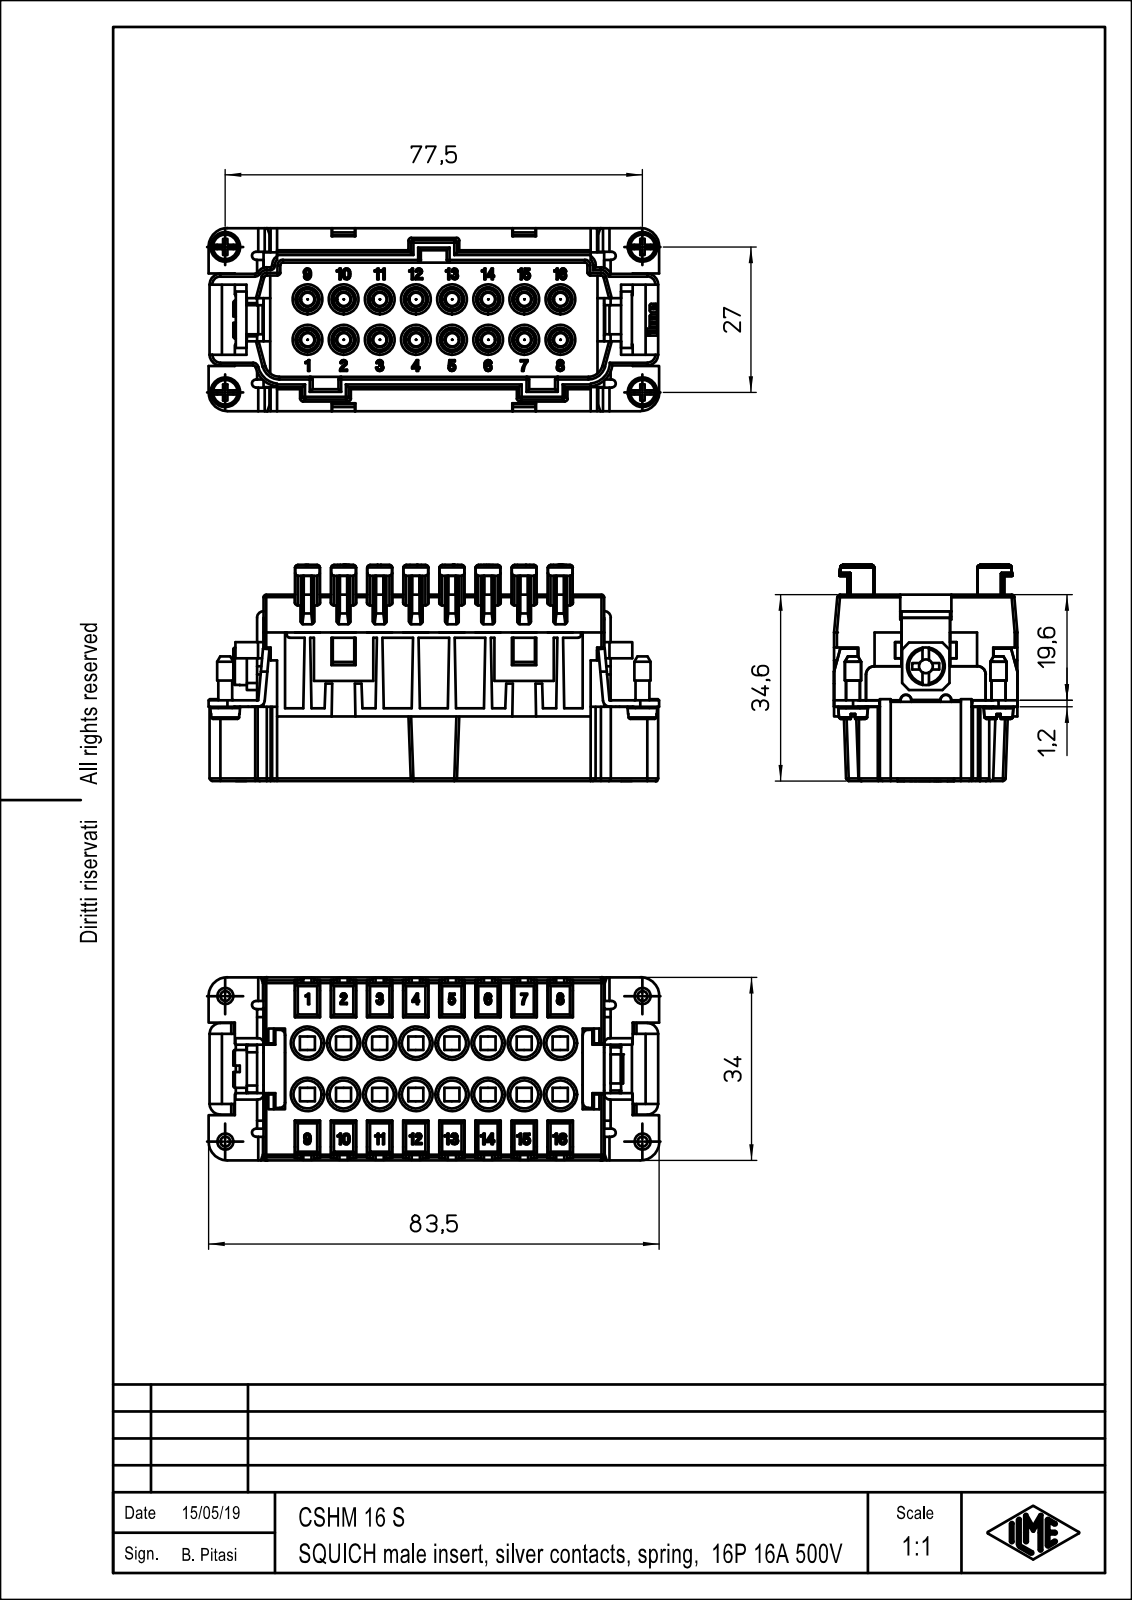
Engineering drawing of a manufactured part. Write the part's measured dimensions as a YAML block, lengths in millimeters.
part_name: "CSHM_16_S"
step_written_by: "Creo Elements/Direct Modeling 20.1B 02-Apr-2019 (C) Parametric Technology GmbH (AUTOMOTIVE_DESIGN)"
units: millimeters
bodies: {solids: 1, faces: 2082, planar: 1264, cylindrical: 557, other: 261}
overall_size: [83.6, 40.1, 34]
volume: 48900
surface_area: 30929
round_holes:
  - {diameter: 5.2, count: 16}
  - {diameter: 2.8, count: 4}
  - {diameter: 2.58, count: 1}
  - {diameter: 4.2, count: 1}
round_bosses_or_shafts:
  - {diameter: 2.48, count: 16}
  - {diameter: 5.5, count: 4}
  - {diameter: 3, count: 4}
  - {diameter: 2.6, count: 4}
  - {diameter: 7, count: 1}
  - {diameter: 6, count: 1}
  - {diameter: 4, count: 1}
partial_cylinders:
  - {radius: 0.5, count: 169}
  - {radius: 0.3, count: 35}
  - {radius: 1.15, count: 16}
  - {radius: 1, count: 12}
  - {radius: 2, count: 10}
  - {radius: 1.2, count: 6}
  - {radius: 0.75, count: 4}
  - {radius: 3.5, count: 4}
face_to_face_distances: [1.5, 26.1, 4.9, 27.6, 20.1, 6.7, 6.4, 1.2, 4, 12.5]
hole_center_spacings: [6.7, 11.62, 13.4, 16.43, 20.1, 22.23, 9.5, 26.8]
